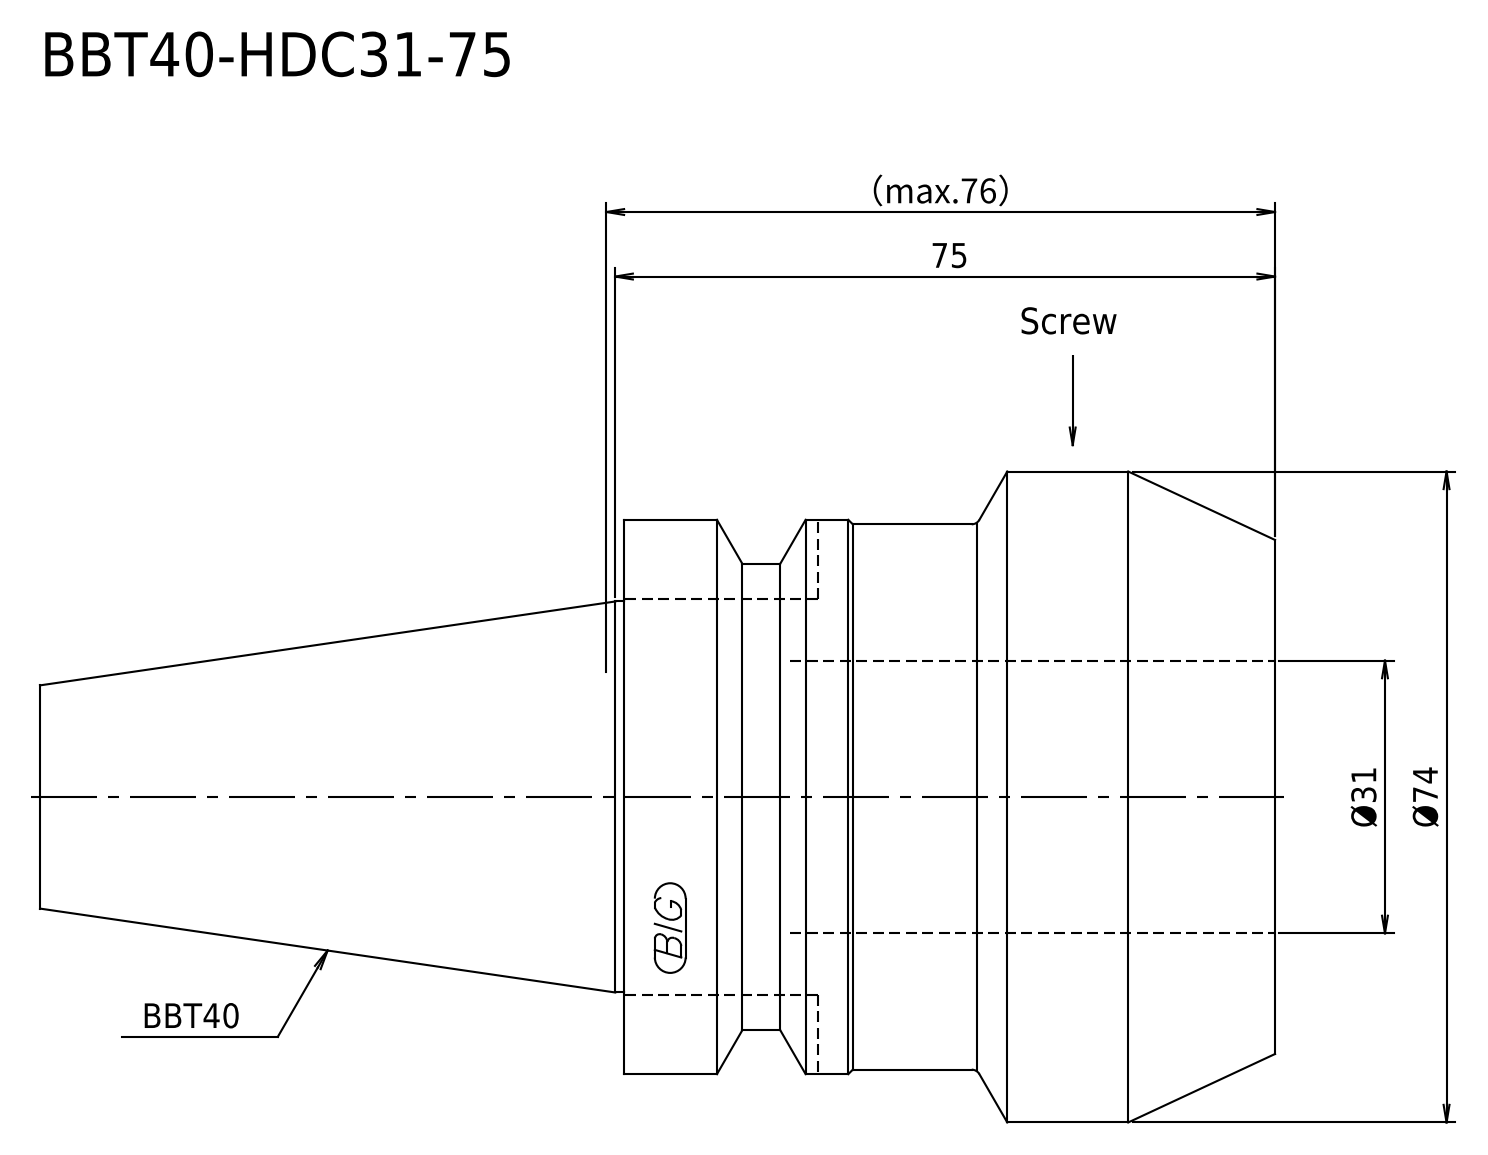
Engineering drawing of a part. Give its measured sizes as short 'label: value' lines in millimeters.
written by: Kubotek KeyCreator V8.5.1 (14335) (CONFIG_CONTROL_DESIGN)
unit: mm
bodies: 1 solid, 17 faces (6 planar, 5 cylindrical, 6 other)
size: 140.4 × 74 × 74
volume: 312 701 mm³; area: 29 408 mm²
bosses: 1× ⌀74, 1× ⌀63, 1× ⌀53, 1× ⌀44.45
face distances: 74, 0.7, 73.3, 140.4, 139.7, 66.4, 55.9, 55.2, 18.1, 84.5
